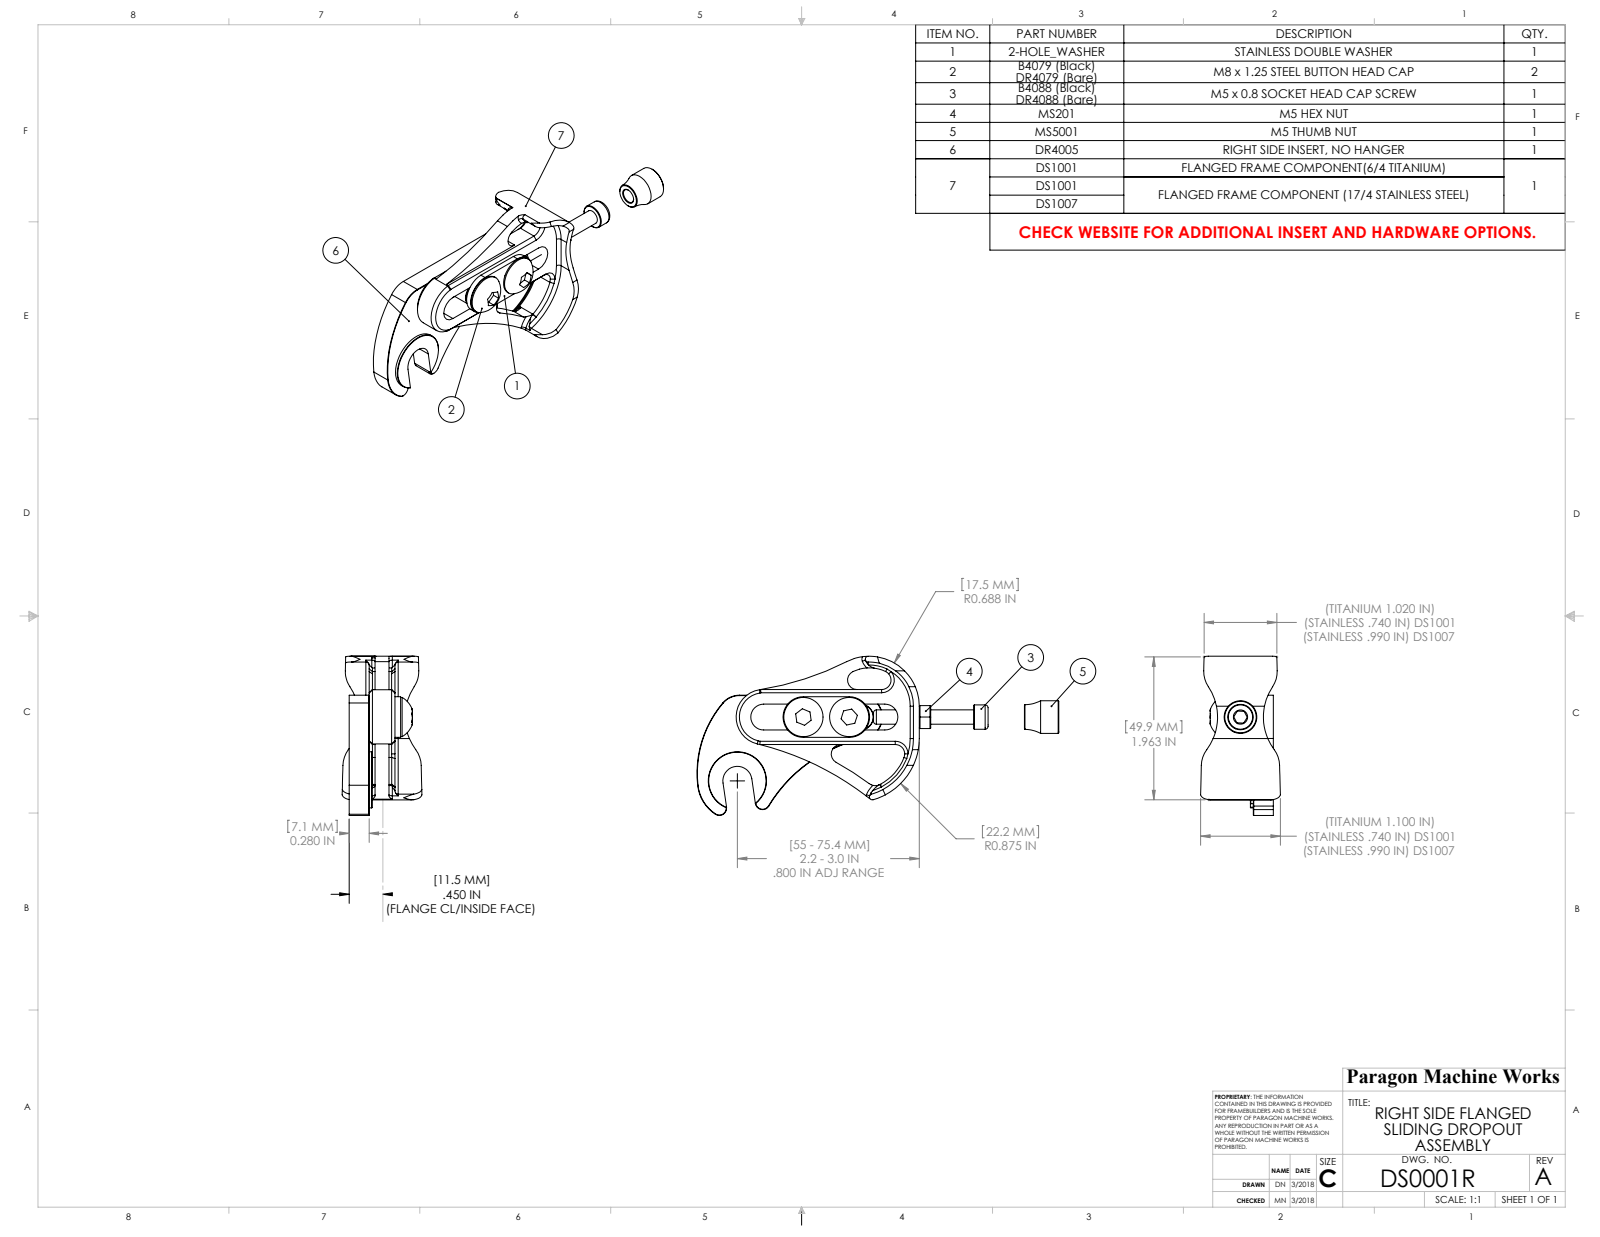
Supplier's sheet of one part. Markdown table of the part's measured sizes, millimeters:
| quantity | value |
| --- | --- |
| part name | DS0001R; PA0001; DR4005; MS5001 (+4 more) |
| STEP written by | SolidWorks 2012 (AUTOMOTIVE_DESIGN) |
| units | millimeters |
| bodies | 8 solids, 272 faces (79 planar, 107 cylindrical, 86 other) |
| overall size | 126.3 × 55.6 × 27.9 |
| volume | 28 220 mm³ |
| surface area | 17 710 mm² |
| round holes (diameter × count) | 7.9 × 2, 8.3 × 2, 4.2 × 1, 5 × 1, 8.5 × 1 |
| round bosses / shafts (diameter × count) | 13.7 × 2, 8 × 2, 20.3 × 1, 11.4 × 1 |
| partial cylindrical surfaces (radius × count) | 0.3 × 12, 3.3 × 4, 4.5 × 4, 9.5 × 4, 5.1 × 3, 7.6 × 3, 1 × 2, 1.1 × 2 |
| main face-to-face distances | 7, 9, 9, 16, 2, 11, 18, 8, 4.1, 2.1 |
| hole center spacings | 16 |
